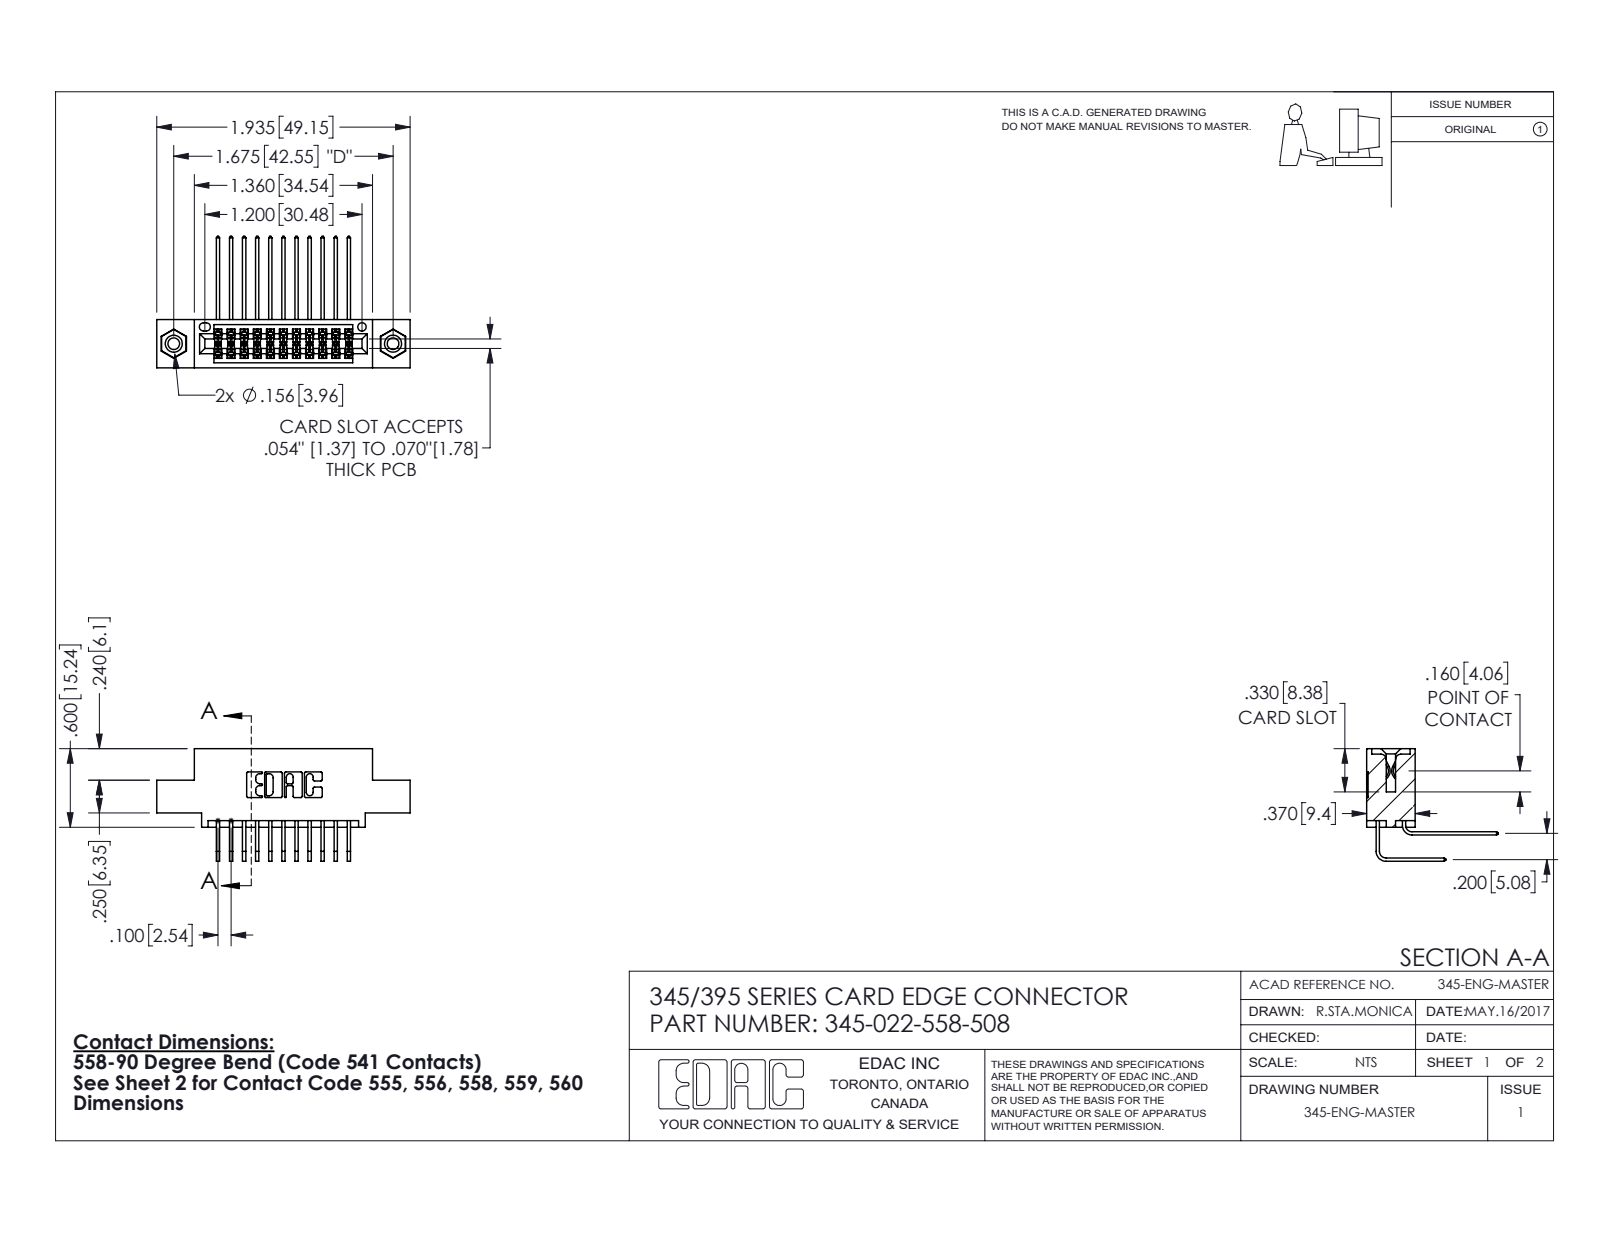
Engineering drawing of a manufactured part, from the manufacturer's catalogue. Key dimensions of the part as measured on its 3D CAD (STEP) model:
Part name (STEP PRODUCT): 345-292-001_558 559 Tail - 1; 345 Part_0.110 Offset - 0.156 Dia-TI; 345-250-001_345-250-003-102; 345-022-558-508 (+1 more)
STEP written by: SolidWorks 2016 (CONFIG_CONTROL_DESIGN)
Units: inches
Bodies: 25 solids, 1334 faces (886 planar, 432 cylindrical, 16 other)
Overall size (bounding box): 1.935 × 1.005 × 0.859
Volume: 0.277 in³ · Surface area: 10.55 in²
Round holes (diameter × count): ⌀0.089 ×2, ⌀0.125 ×2, ⌀0.156 ×2, ⌀0.064 ×1
Round bosses / shafts (diameter × count): ⌀0.155 ×2
Partial cylindrical surfaces — rounded edges, fillets, slot ends (radius × count): R0.006 ×44, R0.01 ×22, R0.007 ×6, R0.031 ×6, R0.026 ×3, R0.014 ×2, R0.019 ×2, R0.022 ×2
Main face-to-face distances: 0.2, 0.072, 0.298, 0.37, 0.098, 0.272, 0.025, 0.225, 0.1, 0.6
Hole centre spacings: 0.27, 1.443, 1.675
